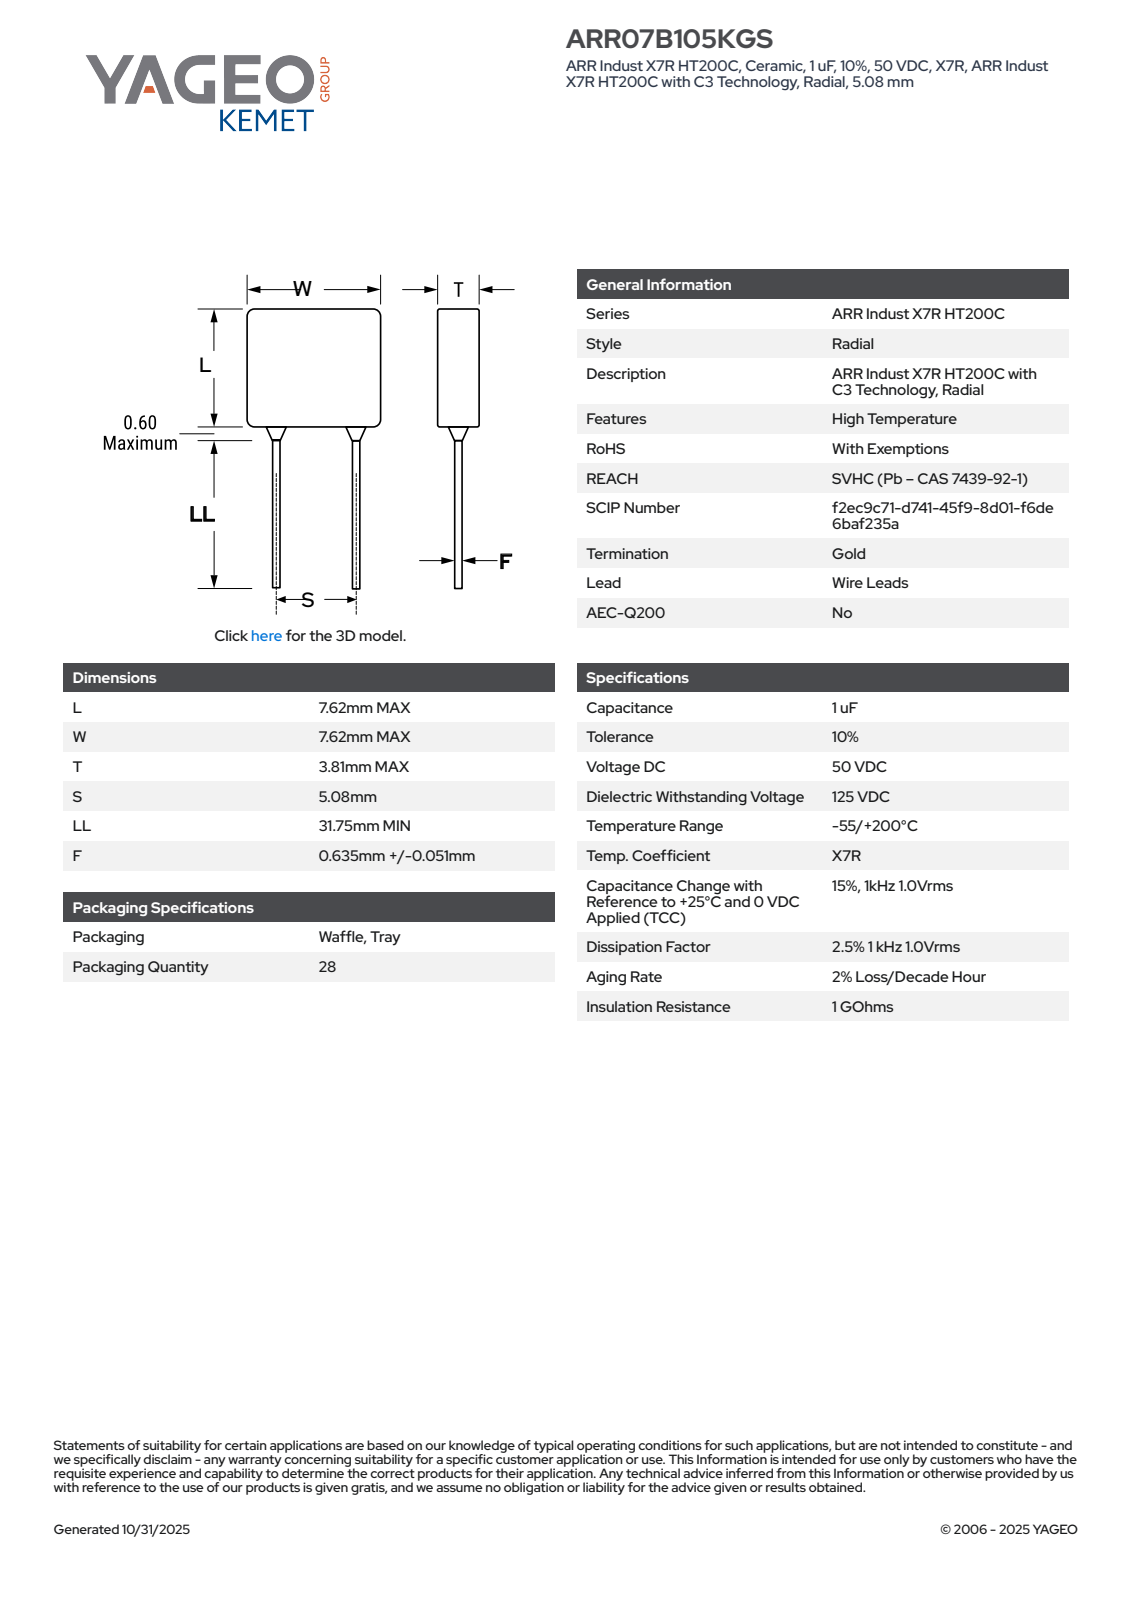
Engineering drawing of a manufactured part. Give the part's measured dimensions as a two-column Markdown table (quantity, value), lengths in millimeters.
| quantity | value |
| --- | --- |
| part name | CCR_C3_7_L7.62T3.81S5.842LL3.175F0.686W7.62 |
| STEP written by | SolidWorks 2021 (AUTOMOTIVE_DESIGN) |
| units | millimeters |
| bodies | 4 solids, 77 faces (65 planar, 8 cylindrical, 4 other) |
| overall size | 11.03 × 7.62 × 3.81 |
| volume | 224 mm³ |
| surface area | 254 mm² |
| round bosses / shafts (diameter × count) | 0.69 × 2 |
| partial cylindrical surfaces (radius × count) | 0.2 × 4 |
| main face-to-face distances | 3.81, 7.62, 3.41, 11.03, 7.72, 4.31, 3.31, 6.56, 3.15, 1.16 |
